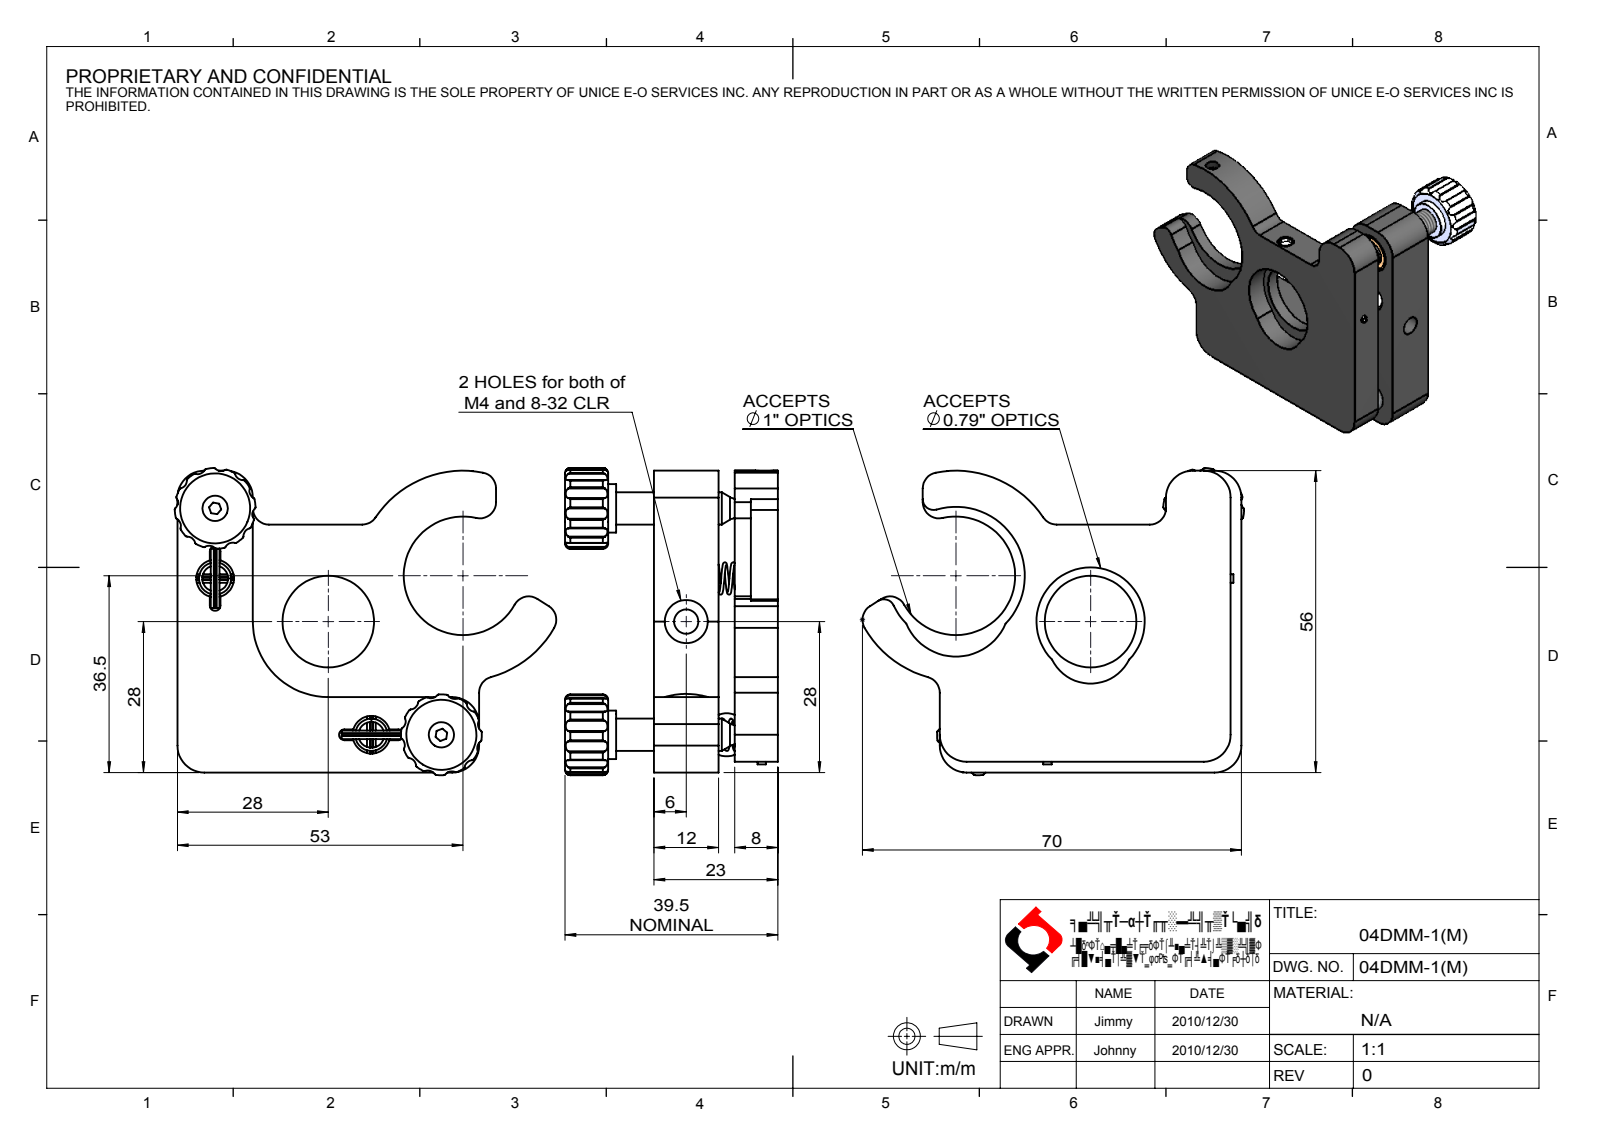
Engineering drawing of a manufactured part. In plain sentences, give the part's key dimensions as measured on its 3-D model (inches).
The part is named "04DMM-1(M)". Its 3-D file was written by "SolidWorks 2016 (CONFIG_CONTROL_DESIGN)". It is 22 solids with 600 faces: 110 planar, 125 cylindrical and 365 other. Overall it measures 2.769 by 2.205 by 1.457 inches. Its volume is 2.07 cubic inches and its surface area 31.71 square inches. Round holes: 4 of diameter 0.047, 2 of diameter 0.067, 2 of diameter 0.13, 2 of diameter 0.157, 2 of diameter 0.177, 2 of diameter 0.276, 2 of diameter 0.311, 2 of diameter 0.315, 2 of diameter 0.374, 1 of diameter 0.236, 1 of diameter 0.669. Round bosses or shafts: 4 of diameter 0.063, 2 of diameter 0.512, 2 of diameter 0.315, 2 of diameter 0.25, 2 of diameter 0.157, 2 of diameter 0.098, 2 of diameter 0.059. Partial cylindrical surfaces (rounded edges, fillets, slot ends): 8 of radius 0.197, 7 of radius 0.118, 4 of radius 0.03, 4 of radius 0.039, 2 of radius 0.079, 1 of radius 0.059, 1 of radius 0.315, 1 of radius 0.394. The main face-to-face distances are 0.315, 0.472, 0.118, 0.591, 0.906, 0.433, 0.079, 0.551, 0.236, 0.709. The hole center spacings are 0.512, 0.635, 0.85, 0.885, 1.169, 1.365, 2.009, 0.316.
